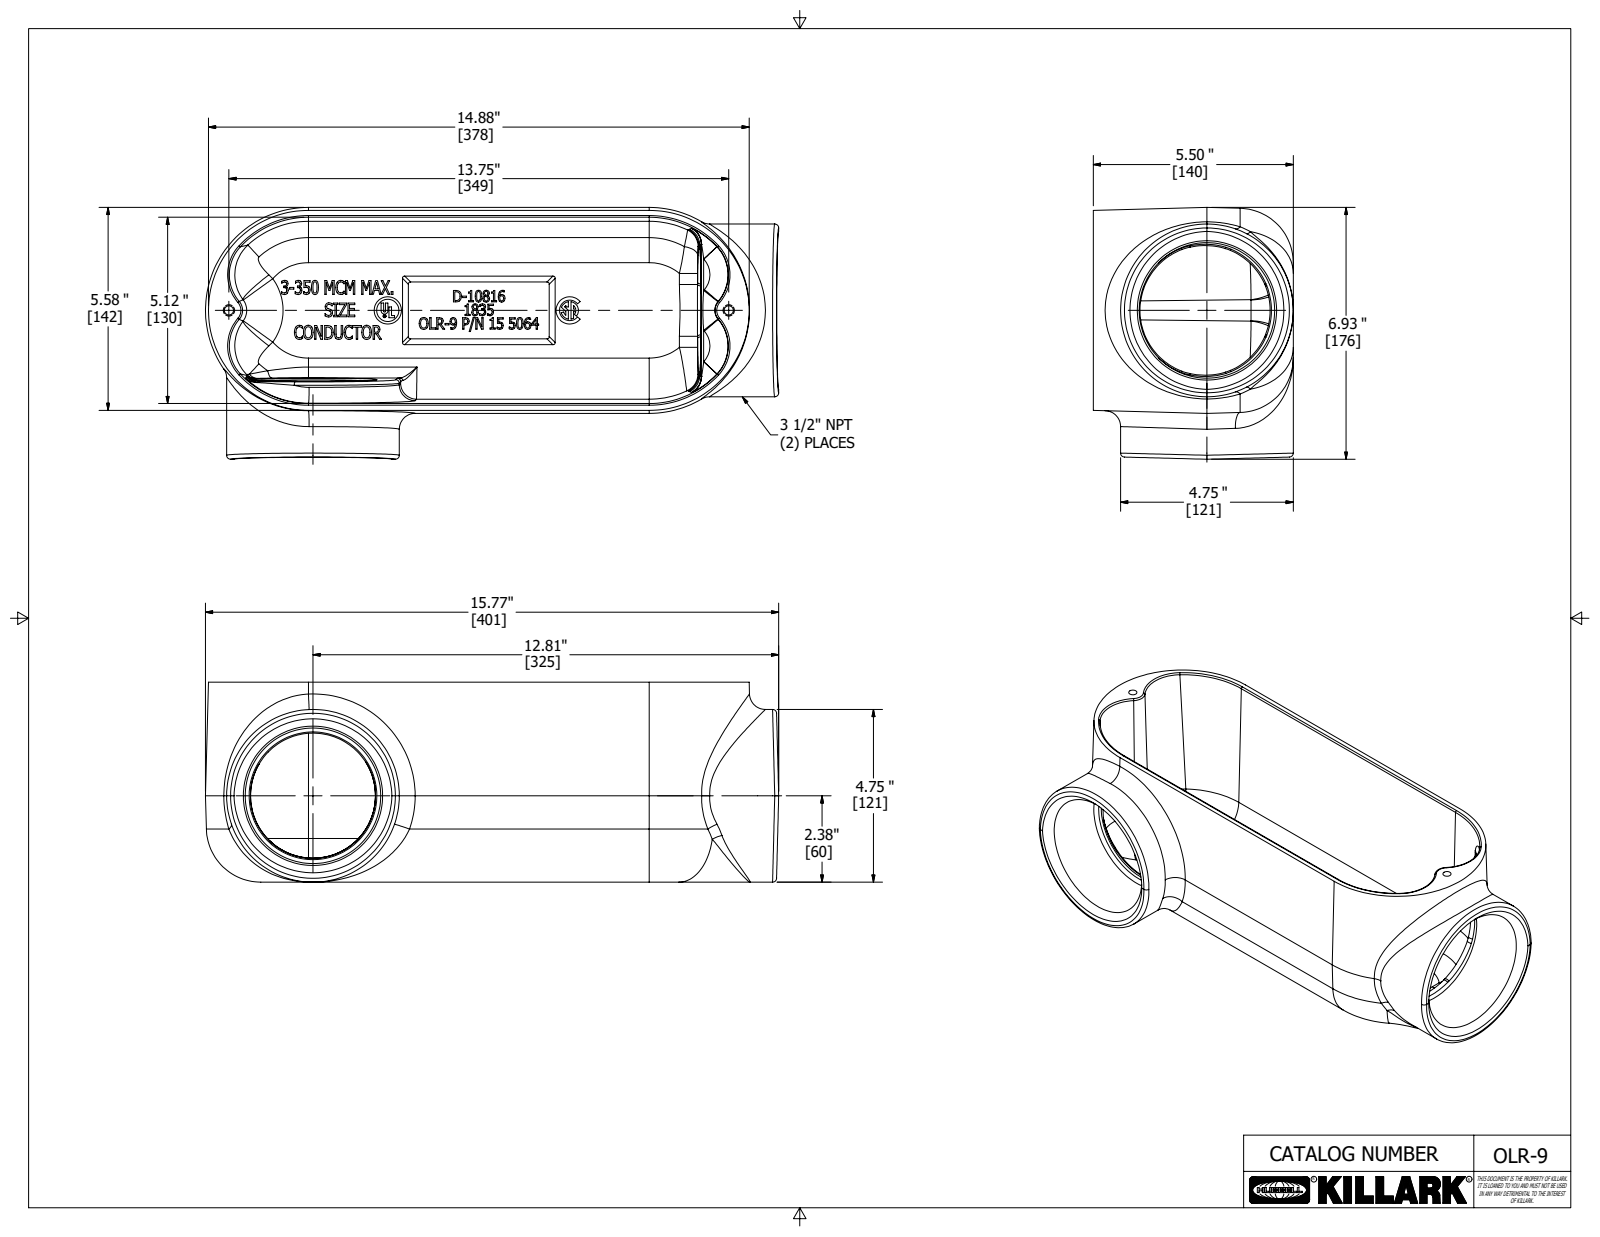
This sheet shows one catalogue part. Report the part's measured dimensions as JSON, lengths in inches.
{"part_name": "10816-1", "step_written_by": "Autodesk Inventor 2018 (AUTOMOTIVE_DESIGN)", "units": "inches", "bodies": {"solids": 1, "faces": 1305, "planar": 669, "cylindrical": 49, "other": 587}, "overall_size": [15.769, 6.925, 5.5], "volume_in3": 88.59, "surface_area_in2": 538.2, "round_holes": [[0.252, 2], [0.07, 1], [0.611, 1]], "round_bosses_or_shafts": [[4.75, 2], [0.75, 1], [0.083, 1]], "partial_cylinders_radius": [[0.031, 8], [0.125, 4], [0.047, 2], [0.375, 2], [1.25, 2], [1.5, 2], [0.008, 1], [0.013, 1]], "face_to_face_distances": [5.313, 0.187, 0.351, 5.664, 5.5, 5.313, 0.094, 0.281, 5.219, 0.025], "hole_center_spacings": [0.183, 4.284, 4.371, 9.379, 9.47, 13.75]}
